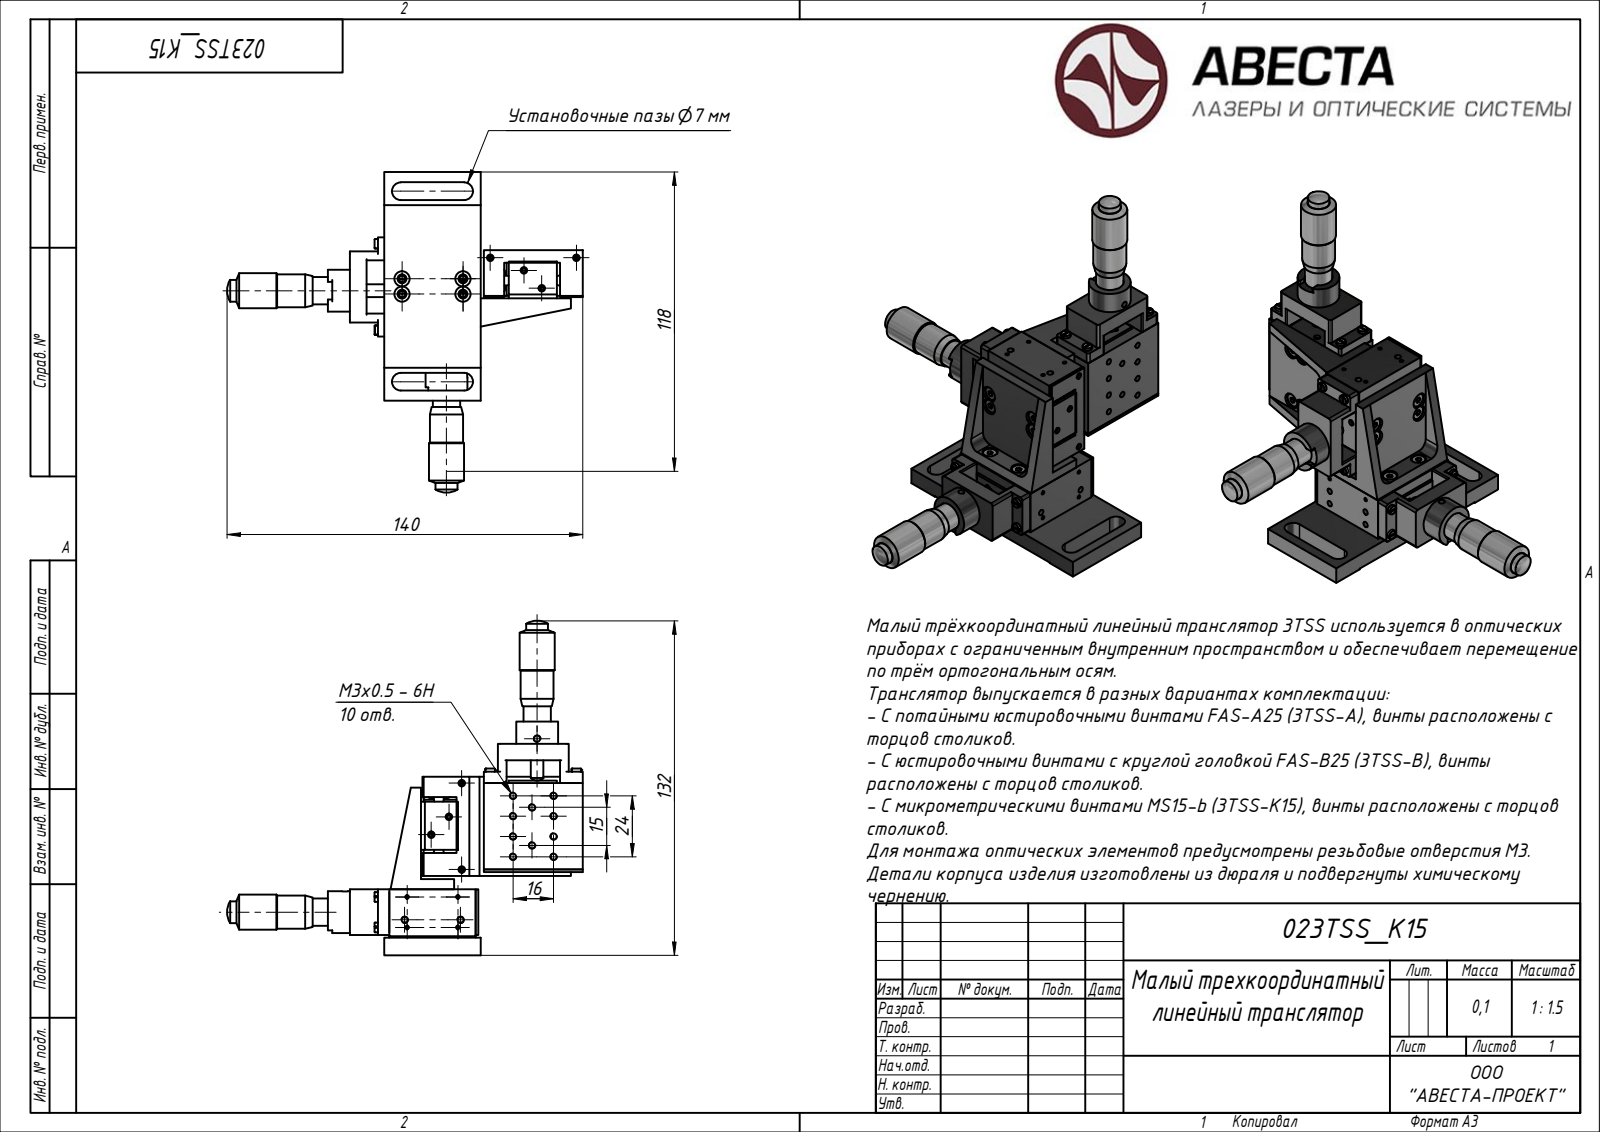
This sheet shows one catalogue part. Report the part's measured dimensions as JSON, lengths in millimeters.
{"step_written_by": "ST-DEVELOPER v15 (AUTOMOTIVE_DESIGN)", "units": "millimeters", "bodies": {"solids": 65, "faces": 1773, "planar": 0, "cylindrical": 0, "other": 1773}, "overall_size": [140.11, 131.69, 126.11]}
